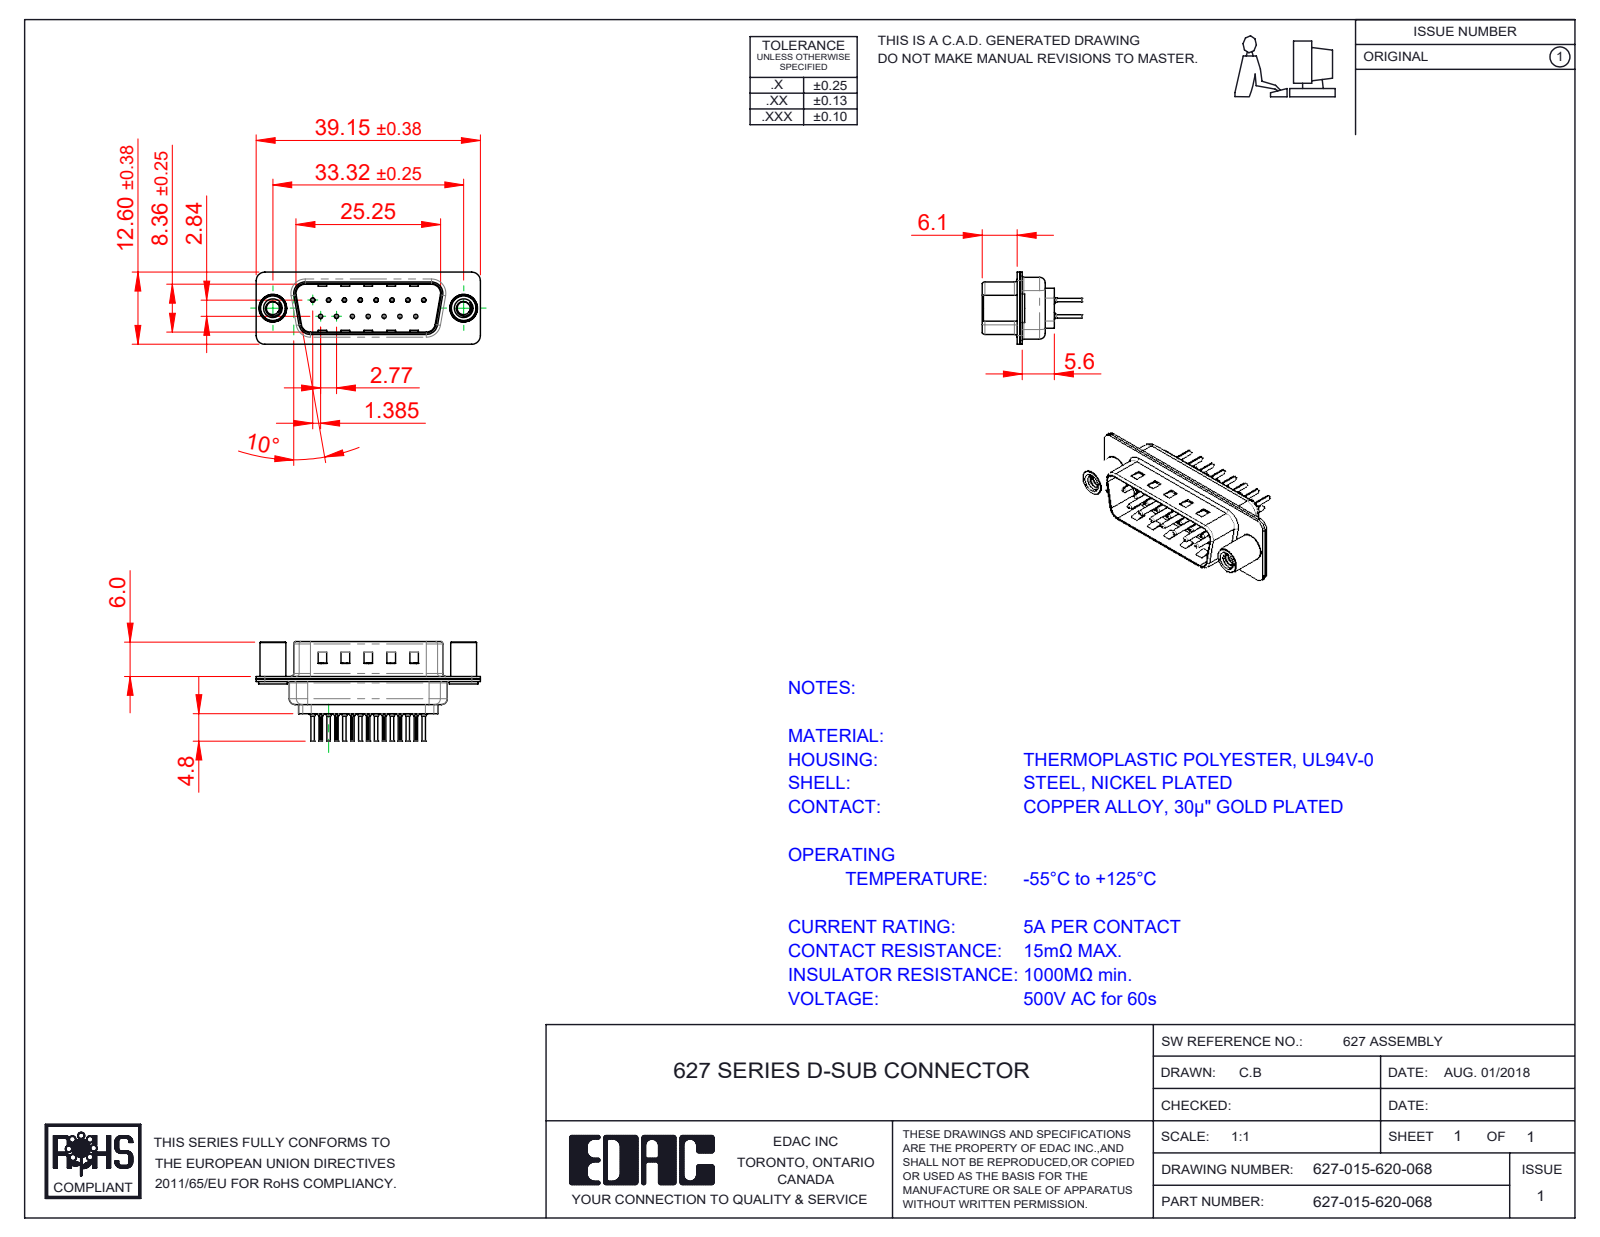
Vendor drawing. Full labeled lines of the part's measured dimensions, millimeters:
Part name (STEP PRODUCT): 627 Shell Front_15 Contacts; 627 4-40 Threaded Standoff; 627 Contact Row 1_20L; 627 Housing_15 LP (+3 more)
STEP written by: SolidWorks 2020 (CONFIG_CONTROL_DESIGN)
Units: millimetres
Bodies: 20 solids, 1844 faces (501 planar, 716 cylindrical, 627 other)
Overall size (bounding box): 39.15 × 17.3 × 12.6
Volume: 1 894 mm³ · Surface area: 5 587 mm²
Round holes (diameter × count): ⌀0.2 ×15, ⌀0.35 ×15, ⌀1.1 ×15, ⌀1.6 ×15, ⌀2.26 ×2, ⌀4 ×2, ⌀4.8 ×2
Round bosses / shafts (diameter × count): ⌀2 ×15, ⌀1.5 ×15, ⌀0.75 ×15, ⌀0.6 ×15, ⌀5 ×2, ⌀4.9 ×2, ⌀4.5 ×2
Partial cylindrical surfaces — rounded edges, fillets, slot ends (radius × count): R0.1 ×30, R1.5 ×16, R2 ×12, R0.5 ×8, R1.6 ×8, R0.25 ×4, R0.6 ×4, R0.65 ×4
Main face-to-face distances: 0.4, 0.45, 0.9, 0.82, 9.58, 8.76, 1.5, 1.4, 6.5, 5.6
Hole centre spacings: 3.16, 2.77, 5.54, 8.31, 11.08, 5.03, 5.04, 7.48
